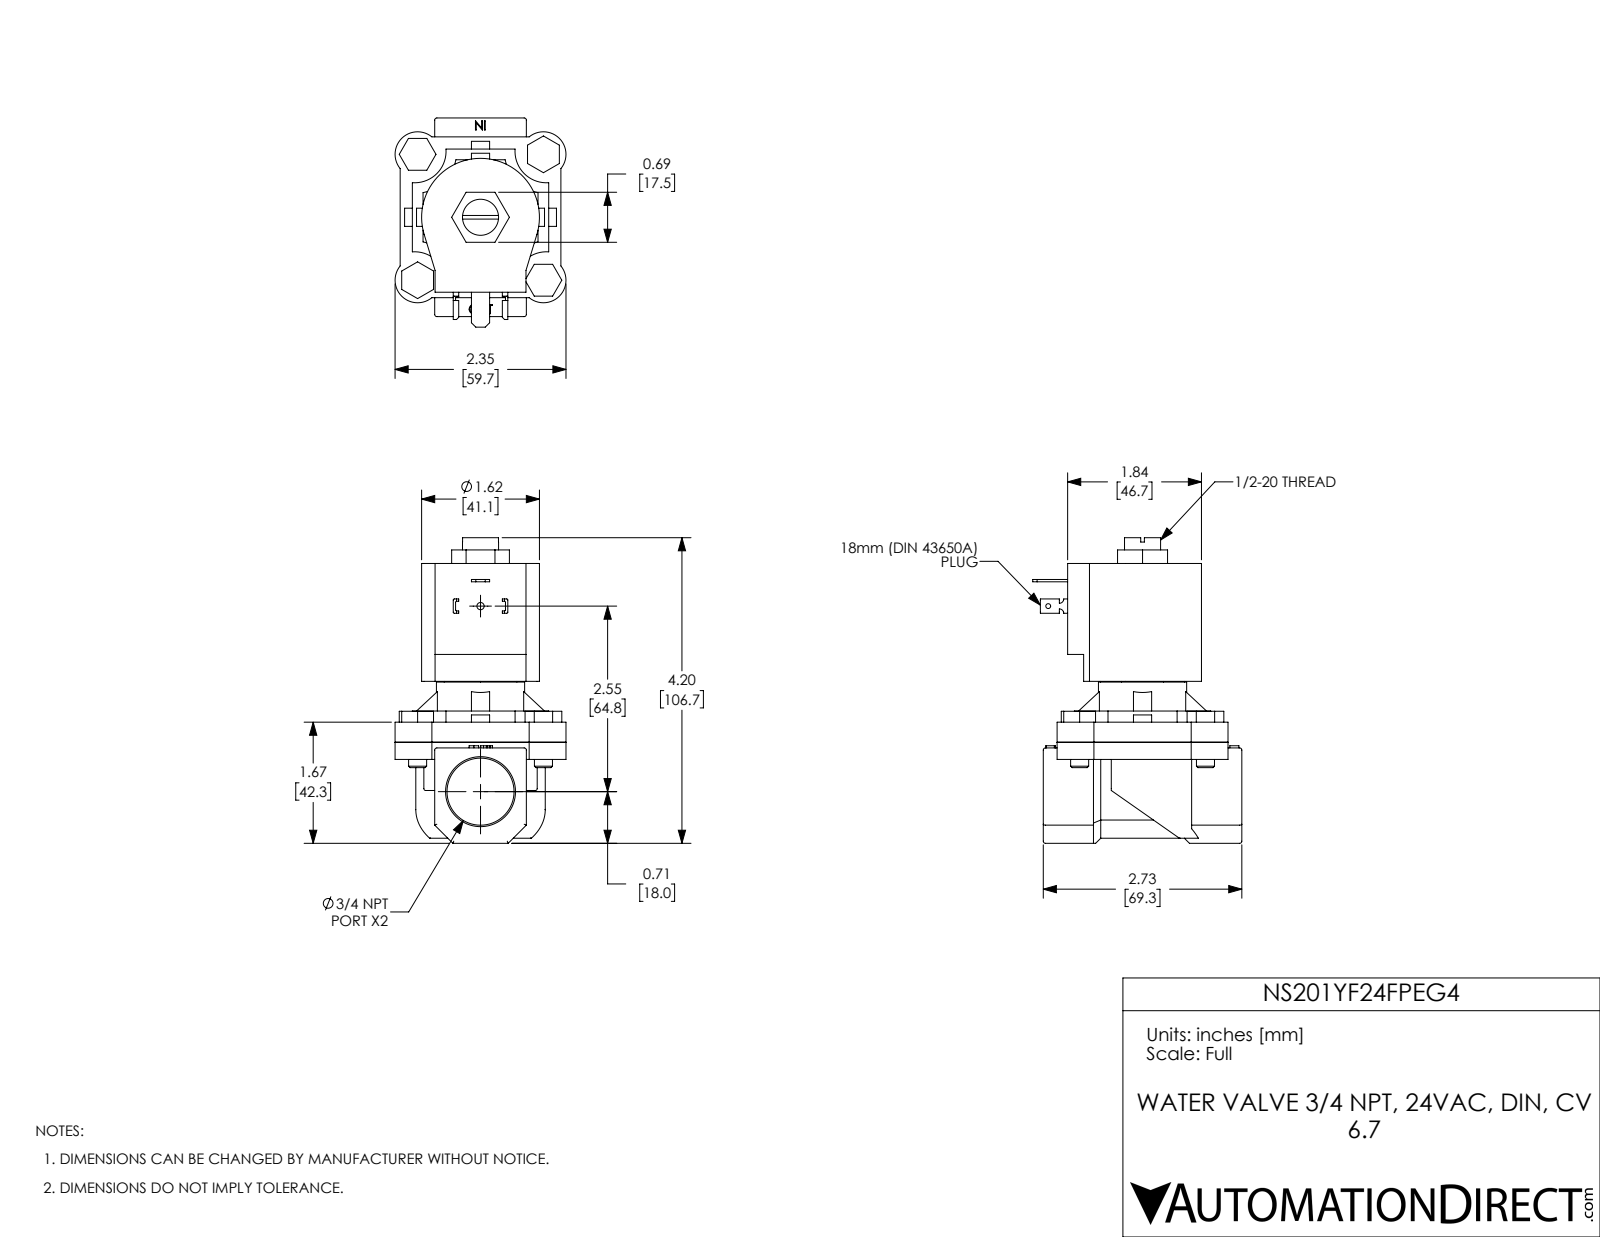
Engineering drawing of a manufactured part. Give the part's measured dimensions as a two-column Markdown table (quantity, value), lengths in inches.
| quantity | value |
| --- | --- |
| part name | NS201YF24FPEG5 |
| STEP written by | SolidWorks 2017 (AUTOMOTIVE_DESIGN) |
| units | inches |
| bodies | 11 solids, 387 faces (241 planar, 113 cylindrical, 33 other) |
| overall size | 4.2 × 2.875 × 2.35 |
| volume | 10.6 in³ |
| surface area | 70.72 in² |
| round holes (diameter × count) | 0.25 × 4, 0.067 × 1, 0.1 × 1, 0.496 × 1, 0.512 × 1, 0.922 × 1, 1.155 × 1 |
| round bosses / shafts (diameter × count) | 0.248 × 4, 1.213 × 1 |
| partial cylindrical surfaces (radius × count) | 0.03 × 15, 0.015 × 8, 0.31 × 4, 0.432 × 4, 0.579 × 4, 0.06 × 2, 0.81 × 1, 0.89 × 1 |
| main face-to-face distances | 0.276, 2.457, 2.181, 0.236, 0.512, 2.693, 0.475, 1.735, 1.26, 2.21 |
| hole center spacings | 1.223, 1.73, 2.446, 2.55 |
